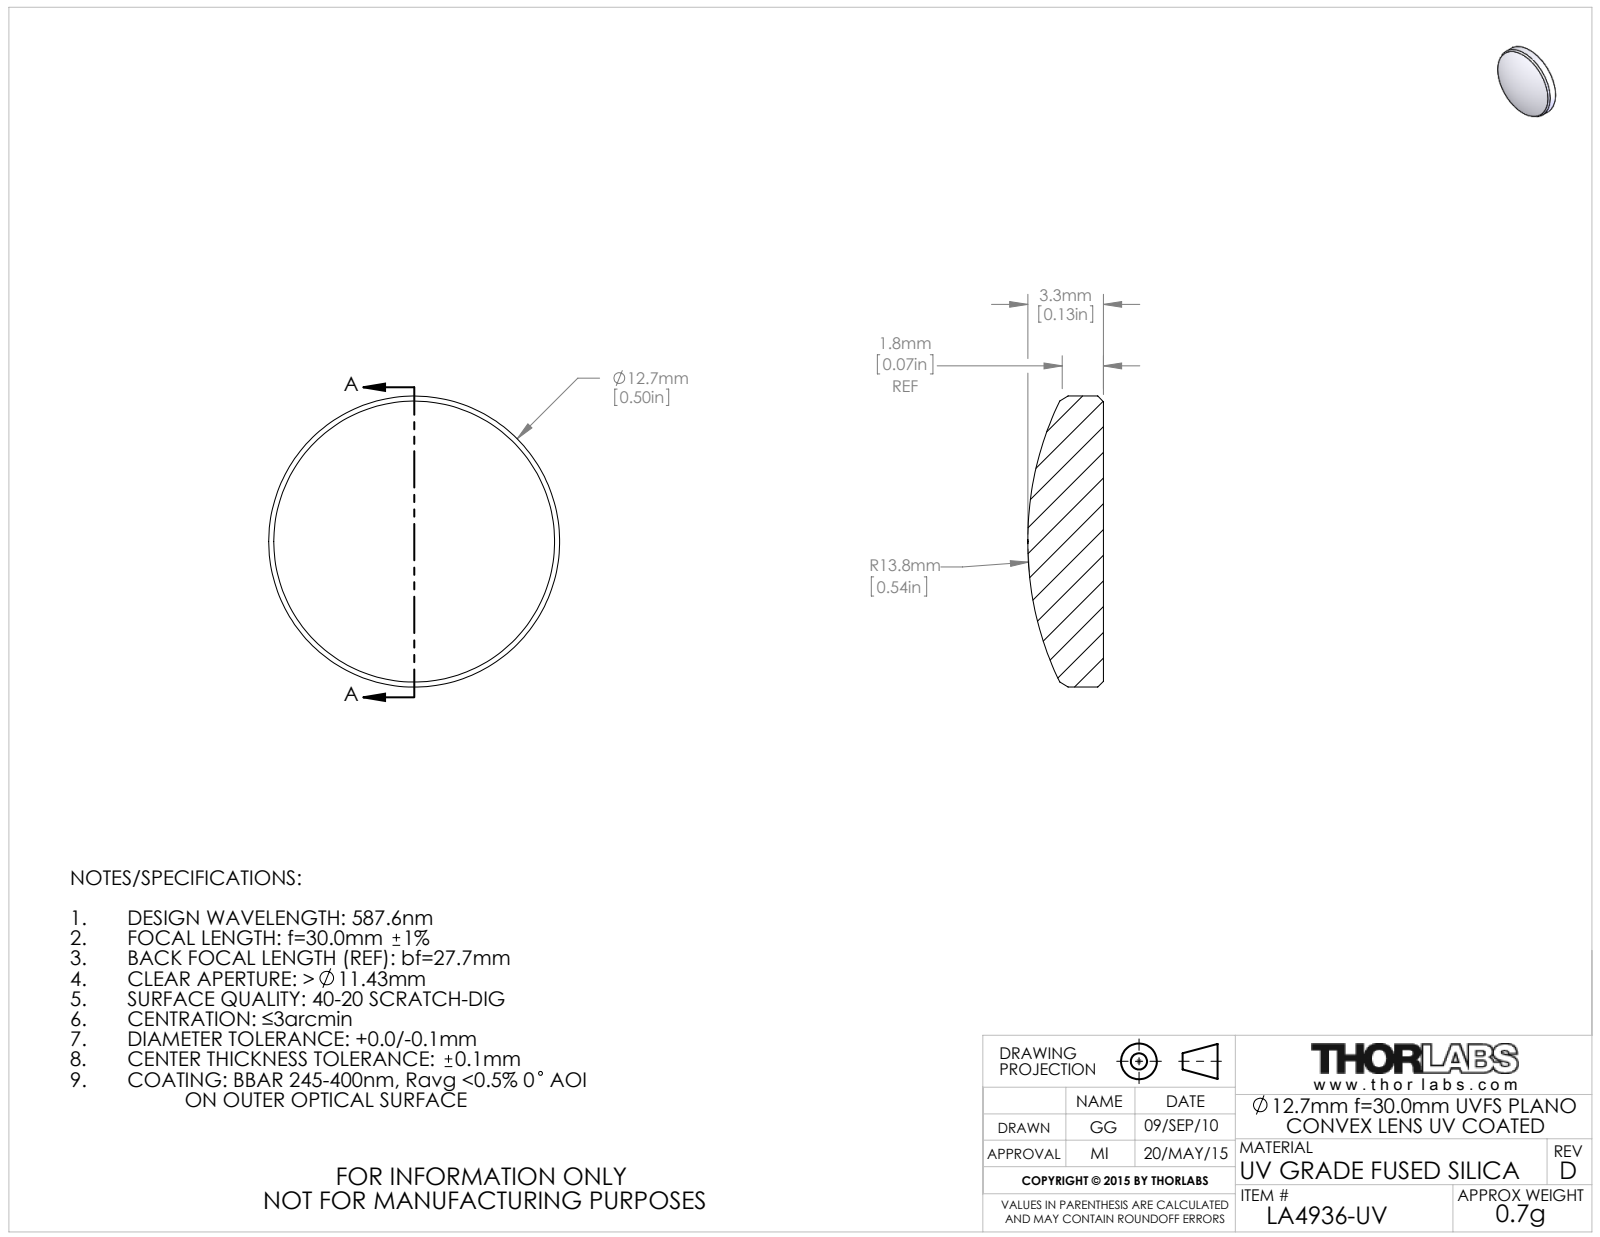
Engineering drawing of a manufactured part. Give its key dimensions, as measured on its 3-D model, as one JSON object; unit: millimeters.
{"part_name": "4273-E0W", "step_written_by": "SolidWorks 2014 (CONFIG_CONTROL_DESIGN)", "units": "millimeters", "bodies": {"solids": 1, "faces": 9, "planar": 1, "cylindrical": 2, "other": 6}, "overall_size": [12.7, 12.7, 3.3], "volume_mm3": 323, "surface_area_mm2": 323, "round_bosses_or_shafts": [[12.7, 1]]}
